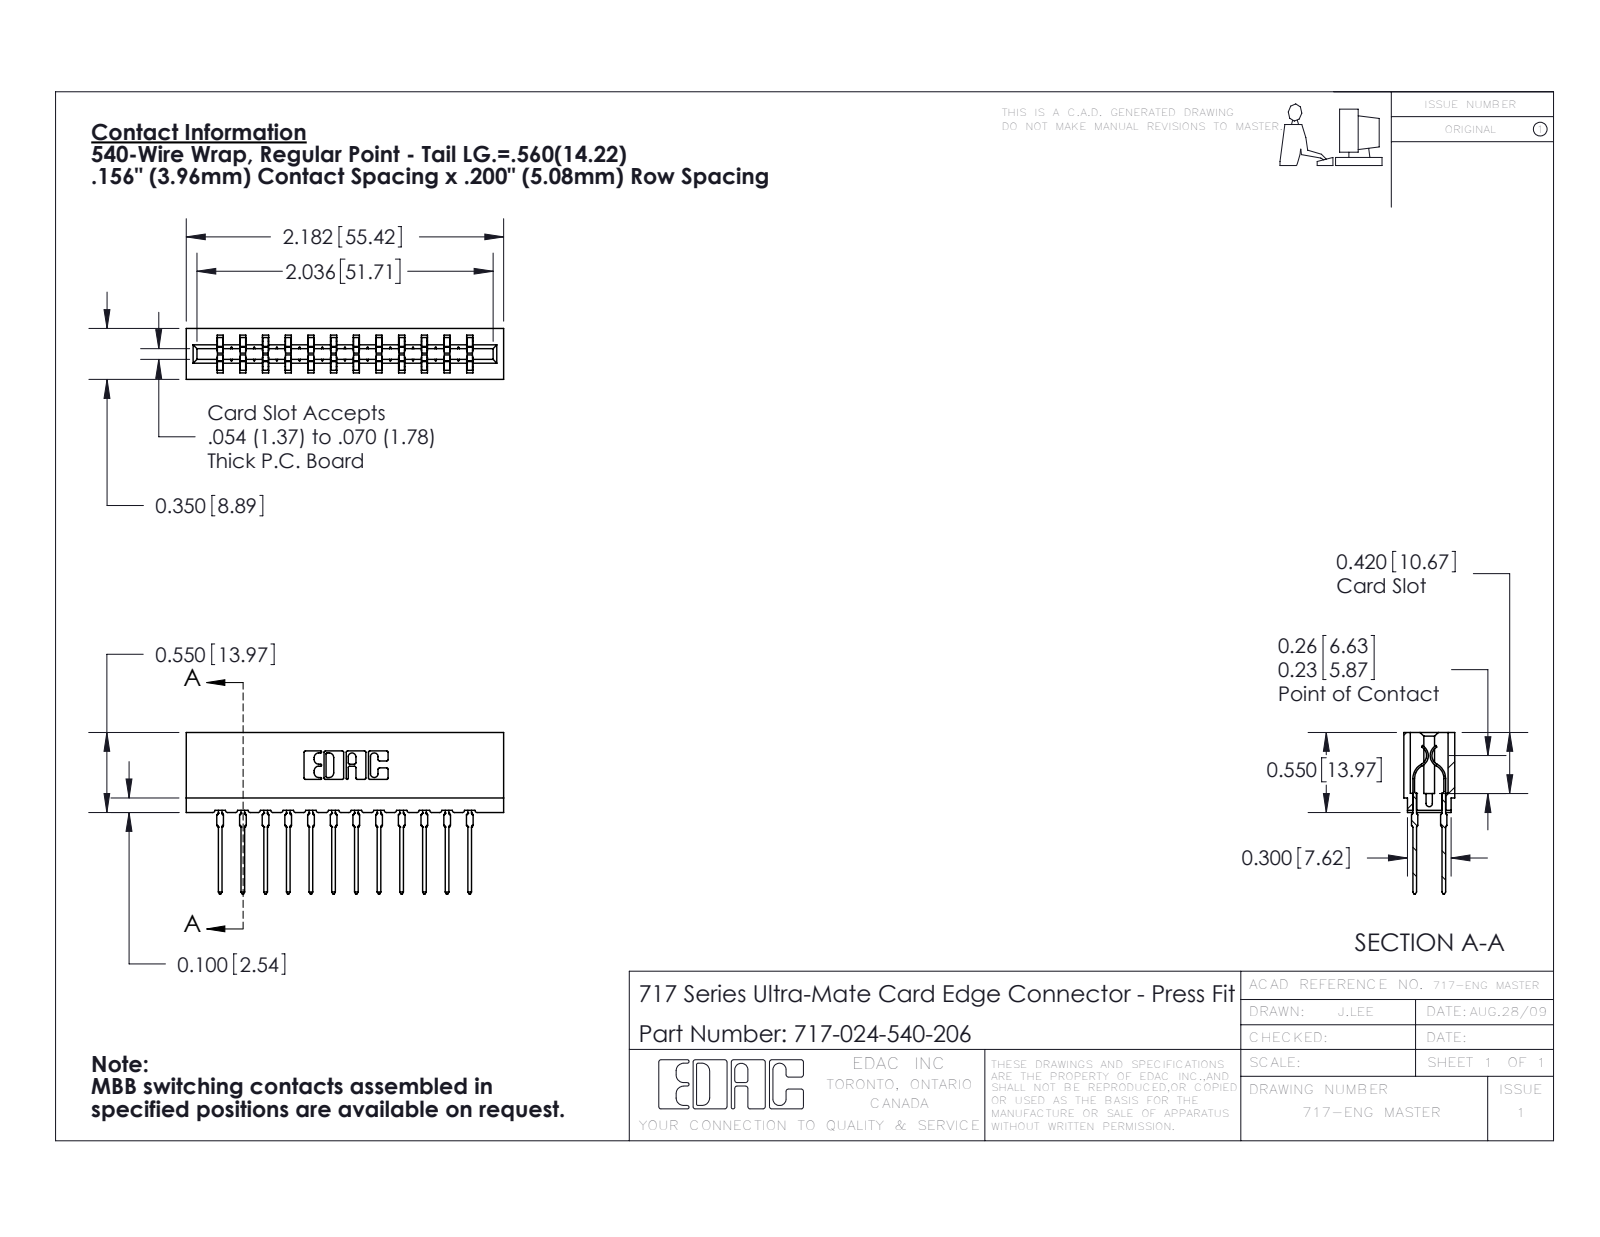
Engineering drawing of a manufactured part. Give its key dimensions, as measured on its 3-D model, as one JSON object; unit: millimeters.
{"part_name": "717 Part_Insulator Option - 06; 745-292-001_540; 717-024-540-206", "step_written_by": "SolidWorks 2016 (CONFIG_CONTROL_DESIGN)", "units": "millimeters", "bodies": {"solids": 25, "faces": 2254, "planar": 1170, "cylindrical": 460, "other": 624}, "overall_size": [55.4, 28.2, 8.9], "volume_mm3": 5000, "surface_area_mm2": 7555, "partial_cylinders_radius": [[0.5, 48], [0.4, 24], [0.3, 22], [0.1, 8], [0.3, 8], [0.2, 6], [0.8, 6], [0.7, 3]], "face_to_face_distances": [5.4, 3.5, 4, 15.8, 8.9, 11.9, 1.6, 7.3, 1.9, 3.8]}
